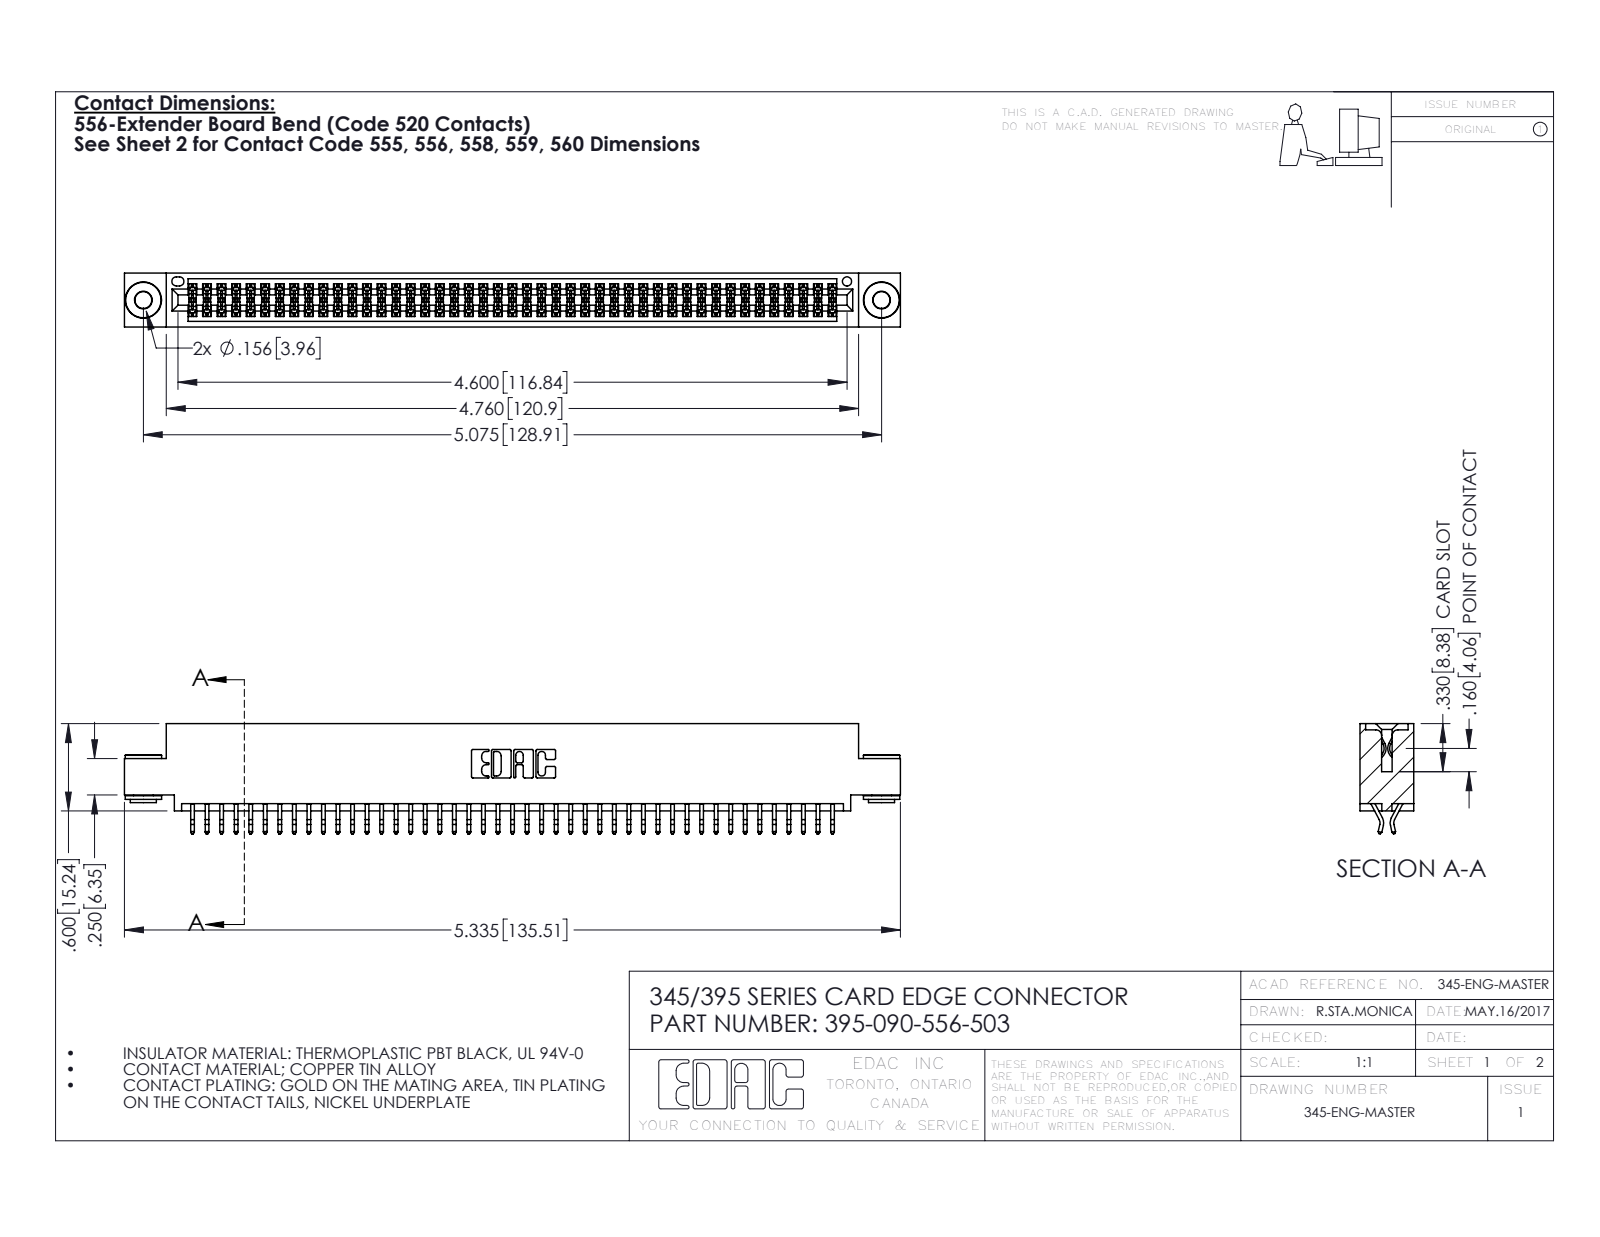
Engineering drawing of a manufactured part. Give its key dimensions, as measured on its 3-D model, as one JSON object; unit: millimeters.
{"part_name": "395-090-556-503; 345 Part_0.110 Offset - 0.156 Dia-TH; 345-292-001_556 Tail; 345-250-002_345-250-002-102", "step_written_by": "SolidWorks 2016 (CONFIG_CONTROL_DESIGN)", "units": "millimeters", "bodies": {"solids": 93, "faces": 5208, "planar": 3424, "cylindrical": 1776, "other": 8}, "overall_size": [135.5, 19.2, 9.4], "volume_mm3": 13100, "surface_area_mm2": 19690, "round_holes": [[2.9, 2], [4, 2], [1.6, 1]], "round_bosses_or_shafts": [[6.4, 2], [4.6, 2], [3.5, 2]], "partial_cylinders_radius": [[0.2, 135], [0.3, 22], [0.2, 6], [0.8, 6], [0.7, 3], [0.3, 2], [0.4, 2], [0.5, 2]], "face_to_face_distances": [1.8, 7.6, 9.4, 5.1, 0.6, 2.5, 6.9, 5.7, 4.4, 3.8], "hole_center_spacings": [6.9, 122.9, 128.9]}
